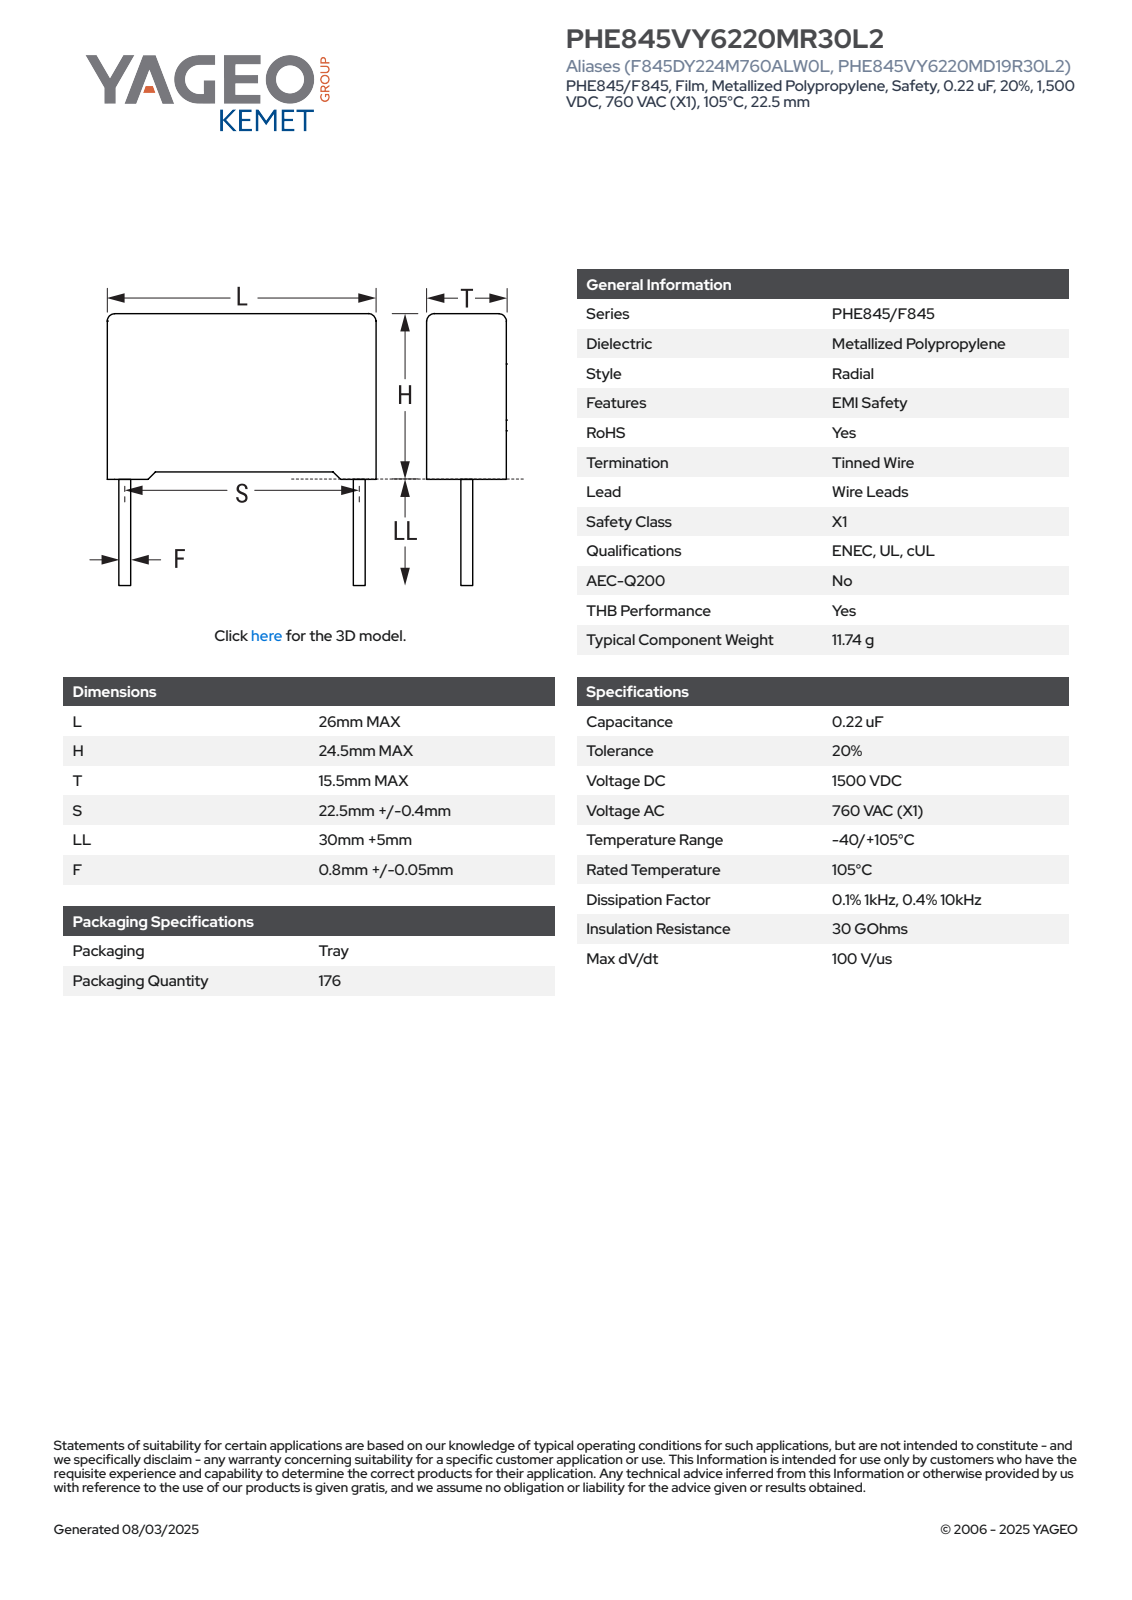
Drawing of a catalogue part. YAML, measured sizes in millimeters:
part_name: "CFR_RB2_26X24.5X15.5_L26H24.5T15.5S22.5LL35F0.85"
step_written_by: "SolidWorks 2021 (AUTOMOTIVE_DESIGN)"
units: millimeters
bodies: {solids: 4, faces: 85, planar: 77, cylindrical: 8, other: 0}
overall_size: [59.5, 26, 15.51]
volume: 9608
surface_area: 3063
round_bosses_or_shafts:
  - {diameter: 0.85, count: 2}
partial_cylinders:
  - {radius: 0.5, count: 4}
face_to_face_distances: [15.5, 26, 23.66, 23.75, 0.75, 0.84, 24.5, 0.87, 25.13, 24.26]
